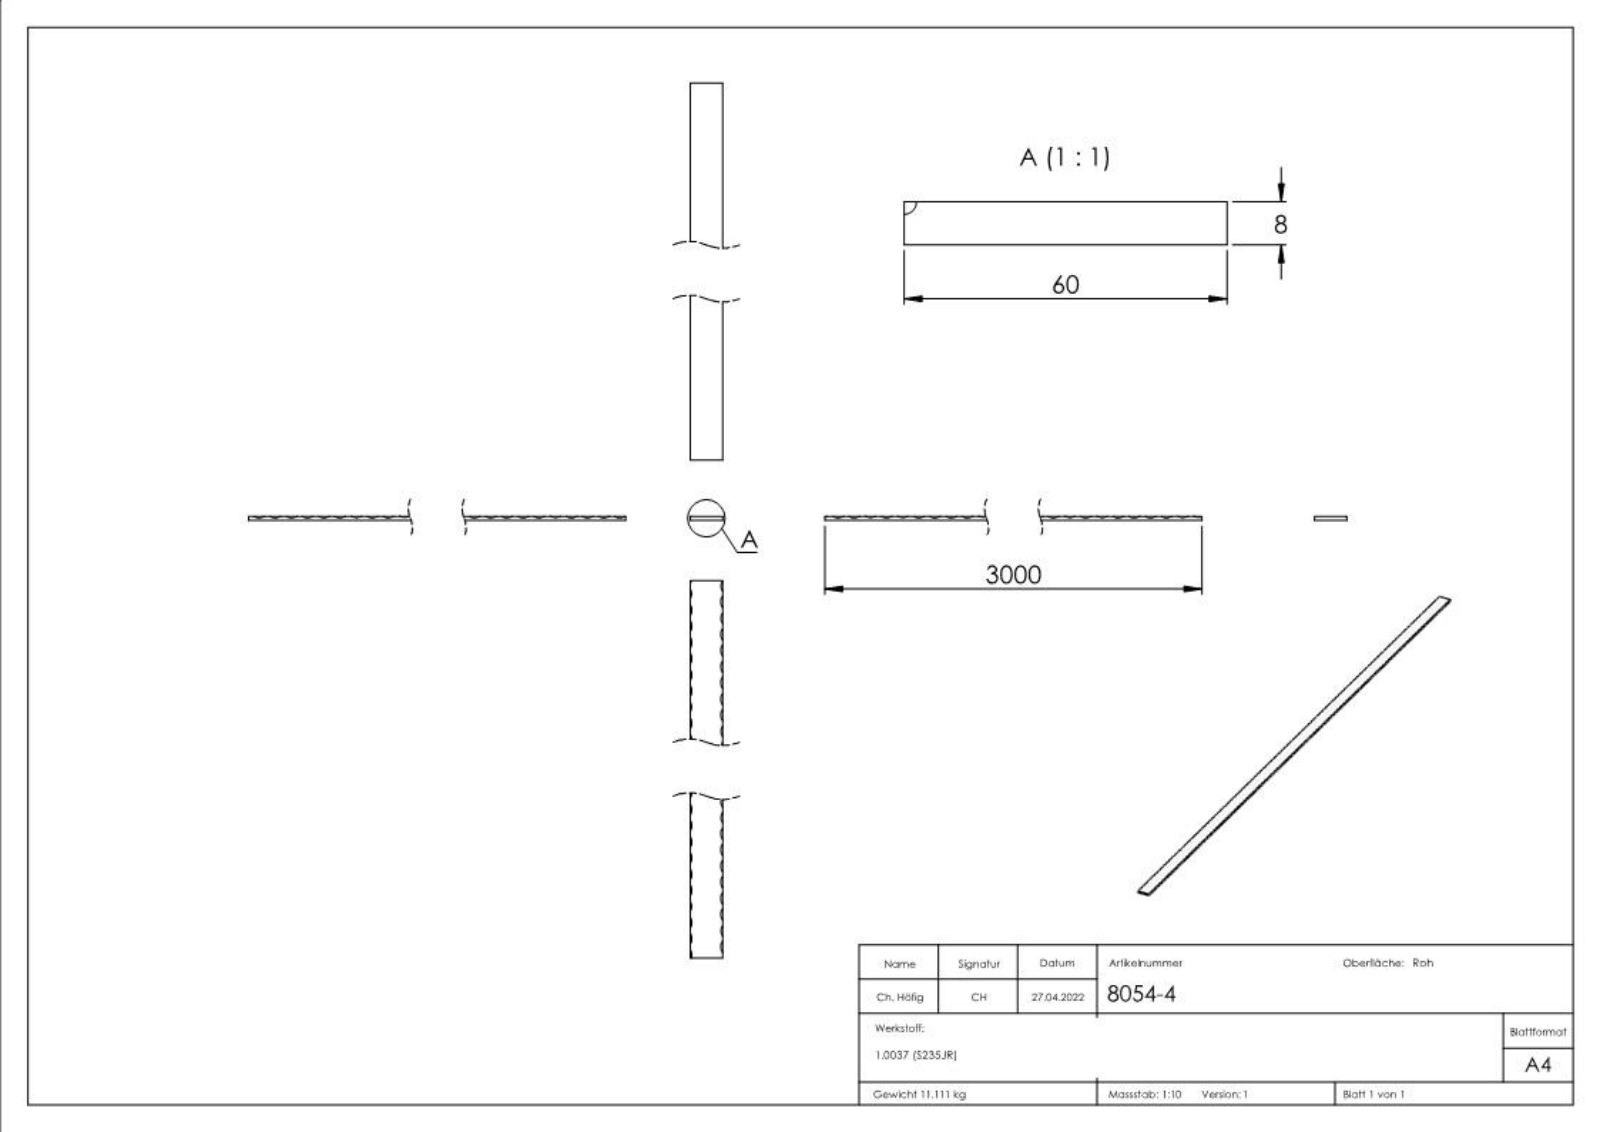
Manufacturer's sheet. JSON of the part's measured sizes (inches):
{"part_name": "8054-4", "step_written_by": "SolidWorks 2018 (CONFIG_CONTROL_DESIGN)", "units": "inches", "bodies": {"solids": 1, "faces": 444, "planar": 141, "cylindrical": 0, "other": 303}, "overall_size": [118.11, 2.362, 0.315], "volume_in3": 86.96, "surface_area_in2": 629.2, "face_to_face_distances": [0.315, 2.362, 118.11, 0.311, 0.124, 0.079, 0.114, 0.129, 0.013, 59.055]}
